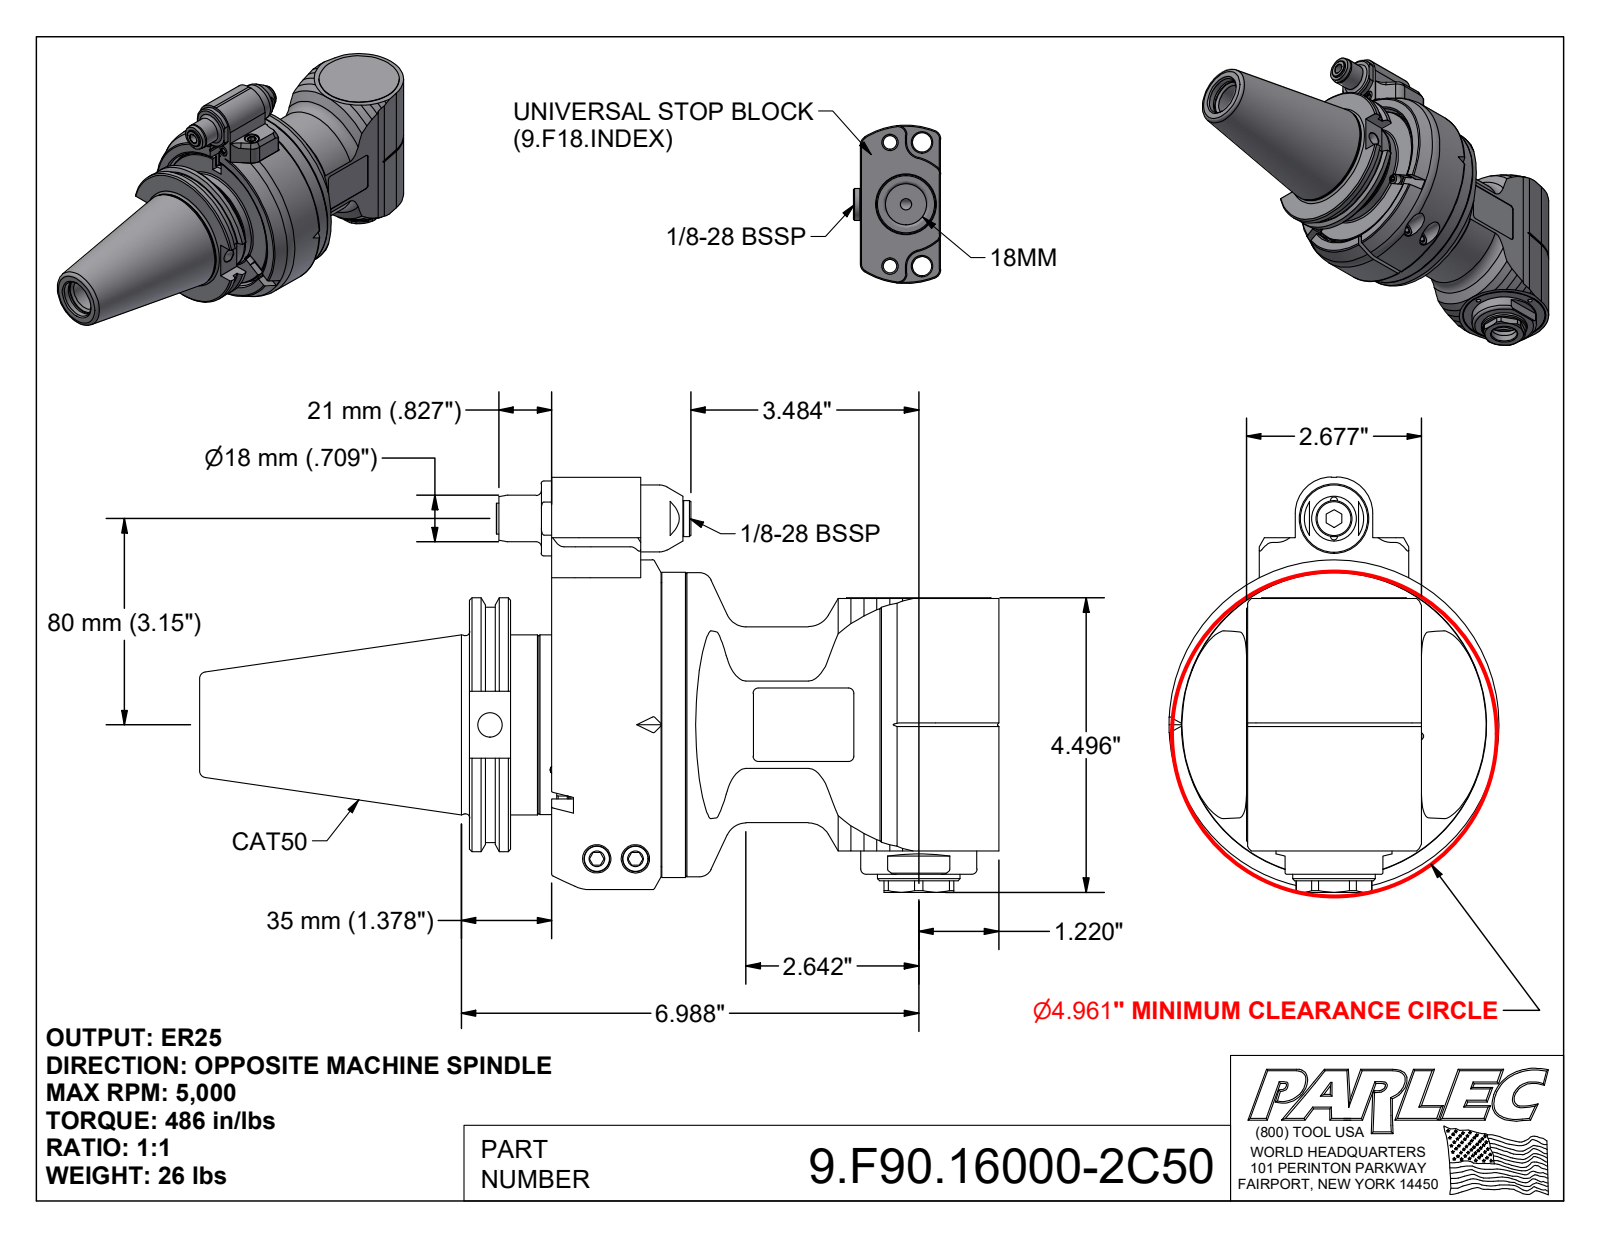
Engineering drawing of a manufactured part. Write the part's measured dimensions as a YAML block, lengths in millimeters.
part_name: "9.F90.16000-2C50; 9GA21C_458 (EVO, Type 2, Cat50, 80mm); 9_F90_16000"
step_written_by: "Autodesk Inventor 2022 (AUTOMOTIVE_DESIGN)"
units: millimeters
bodies: {solids: 4, faces: 659, planar: 271, cylindrical: 181, other: 207}
overall_size: [310.1, 161, 128]
volume: 1704000
surface_area: 208313
round_holes:
  - {diameter: 10.5, count: 20}
  - {diameter: 3.2, count: 4}
  - {diameter: 5, count: 3}
  - {diameter: 6.5, count: 3}
  - {diameter: 12.5, count: 3}
  - {diameter: 2.6, count: 2}
  - {diameter: 3.3, count: 2}
  - {diameter: 4.2, count: 2}
  - {diameter: 8, count: 2}
  - {diameter: 10.4, count: 2}
  - {diameter: 11, count: 2}
  - {diameter: 2.5, count: 1}
round_bosses_or_shafts:
  - {diameter: 10, count: 4}
  - {diameter: 12, count: 3}
  - {diameter: 18, count: 2}
  - {diameter: 6, count: 2}
  - {diameter: 2.5, count: 2}
  - {diameter: 128, count: 1}
  - {diameter: 118.4, count: 1}
  - {diameter: 118, count: 1}
partial_cylinders:
  - {radius: 1, count: 14}
  - {radius: 2, count: 12}
  - {radius: 3, count: 6}
  - {radius: 4, count: 4}
  - {radius: 0.4, count: 2}
  - {radius: 0.5, count: 2}
  - {radius: 3.5, count: 2}
  - {radius: 8, count: 2}
face_to_face_distances: [0.5, 35.5, 1, 6.5, 35, 2, 5, 5.5, 34, 1.5]
hole_center_spacings: [46.75, 56.27, 66.11, 92.59, 93.5, 45.33, 81.78, 13.01]
